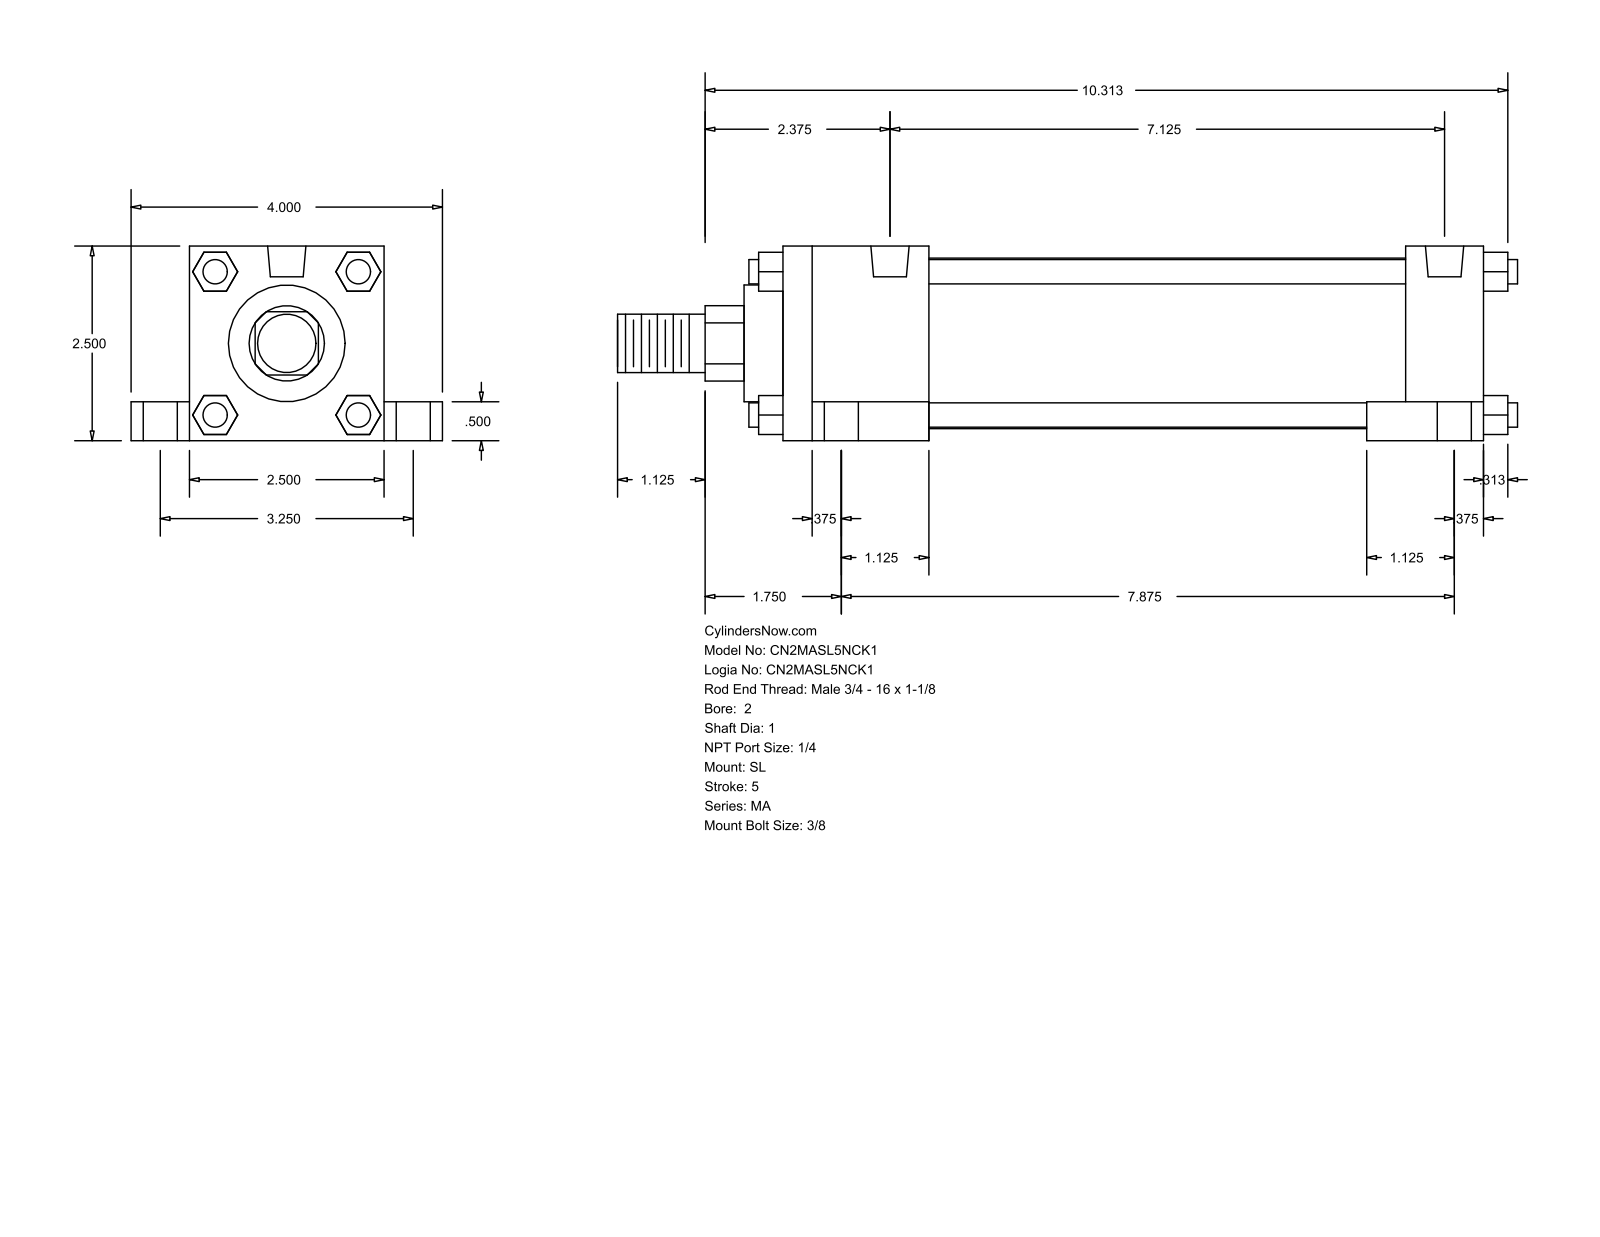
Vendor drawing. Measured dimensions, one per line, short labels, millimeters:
name: MA_SL__0200_1
written by: GSSL Pune (CONFIG_CONTROL_DESIGN)
unit: mm
bodies: 0 solids, 148 faces (112 planar, 36 cylindrical, 0 other)
size: 293.69 × 101.6 × 63.5
holes: 4× ⌀7.94, 4× ⌀11.11, 4× ⌀17.46, 2× ⌀12.49
bosses: 4× ⌀7.94, 1× ⌀55.63, 1× ⌀38.1, 1× ⌀25.4, 1× ⌀19.05
rounds: 1× R12.29
face distances: 63.5, 12.7, 228.6, 19.05, 82.55, 25.4, 50.8, 47.63, 180.97, 203.2
hole spacings: 41.39, 44.22, 82.54, 180.97, 188.71, 200.02, 201.13, 216.38
